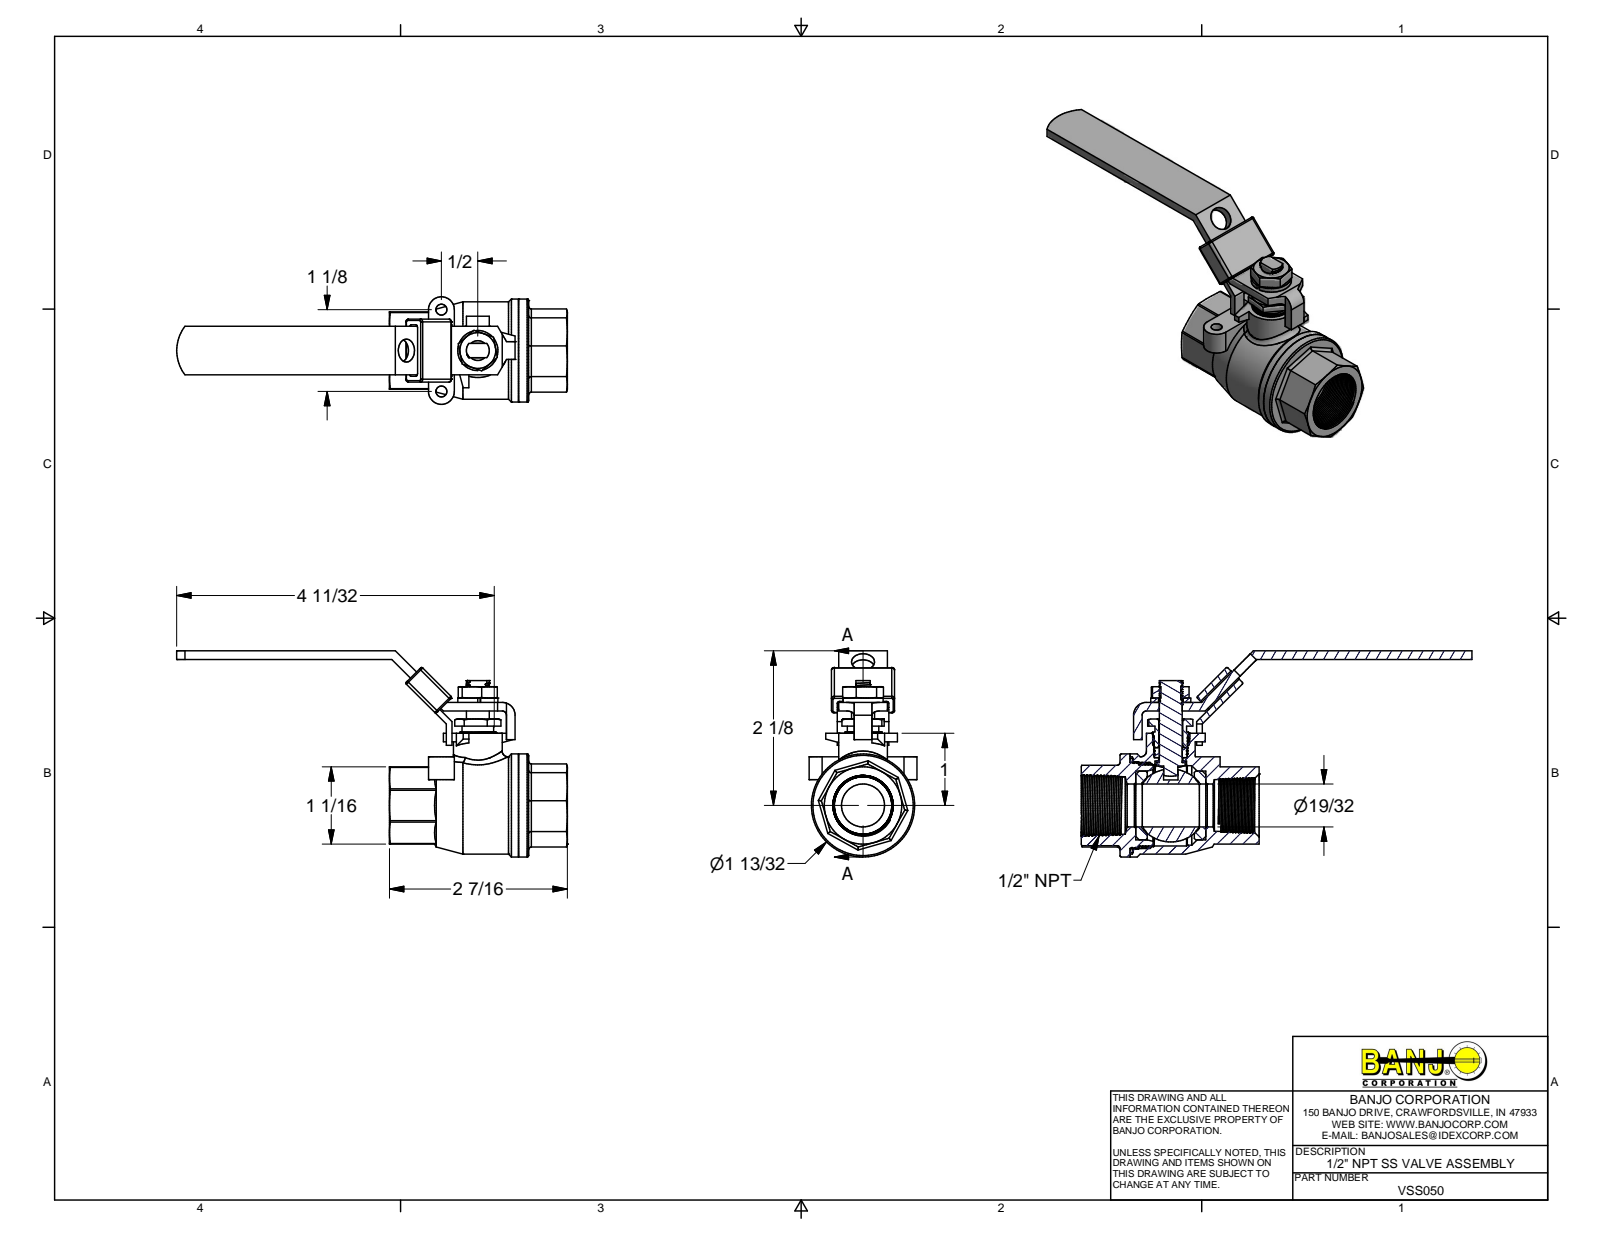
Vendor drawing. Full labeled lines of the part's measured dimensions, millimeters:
Part name (STEP PRODUCT): VSS050
STEP written by: Autodesk Inventor 2013 (AUTOMOTIVE_DESIGN)
Units: millimetres
Bodies: 14 solids, 371 faces (143 planar, 105 cylindrical, 123 other)
Overall size (bounding box): 136.5 × 72 × 37.58
Volume: 42 517 mm³ · Surface area: 32 441 mm²
Round holes (diameter × count): ⌀3.8 ×2, ⌀6.91 ×1, ⌀8 ×1, ⌀8.4 ×1, ⌀8.5 ×1, ⌀8.6 ×1, ⌀11 ×1, ⌀11.5 ×1, ⌀15 ×1, ⌀24 ×1, ⌀27.8 ×1, ⌀28.3 ×1
Round bosses / shafts (diameter × count): ⌀36 ×1, ⌀33 ×1, ⌀30 ×1, ⌀17 ×1, ⌀14 ×1, ⌀12.7 ×1, ⌀11.3 ×1, ⌀10.88 ×1
Partial cylindrical surfaces — rounded edges, fillets, slot ends (radius × count): R1 ×16, R0.5 ×8, R4.5 ×3, R1.5 ×1, R12 ×1, R14 ×1, R14.5 ×1
Main face-to-face distances: 3, 2, 27, 2.5, 5.5, 3.5, 6, 5, 18, 0.5
Hole centre spacings: 19.12, 28.58
